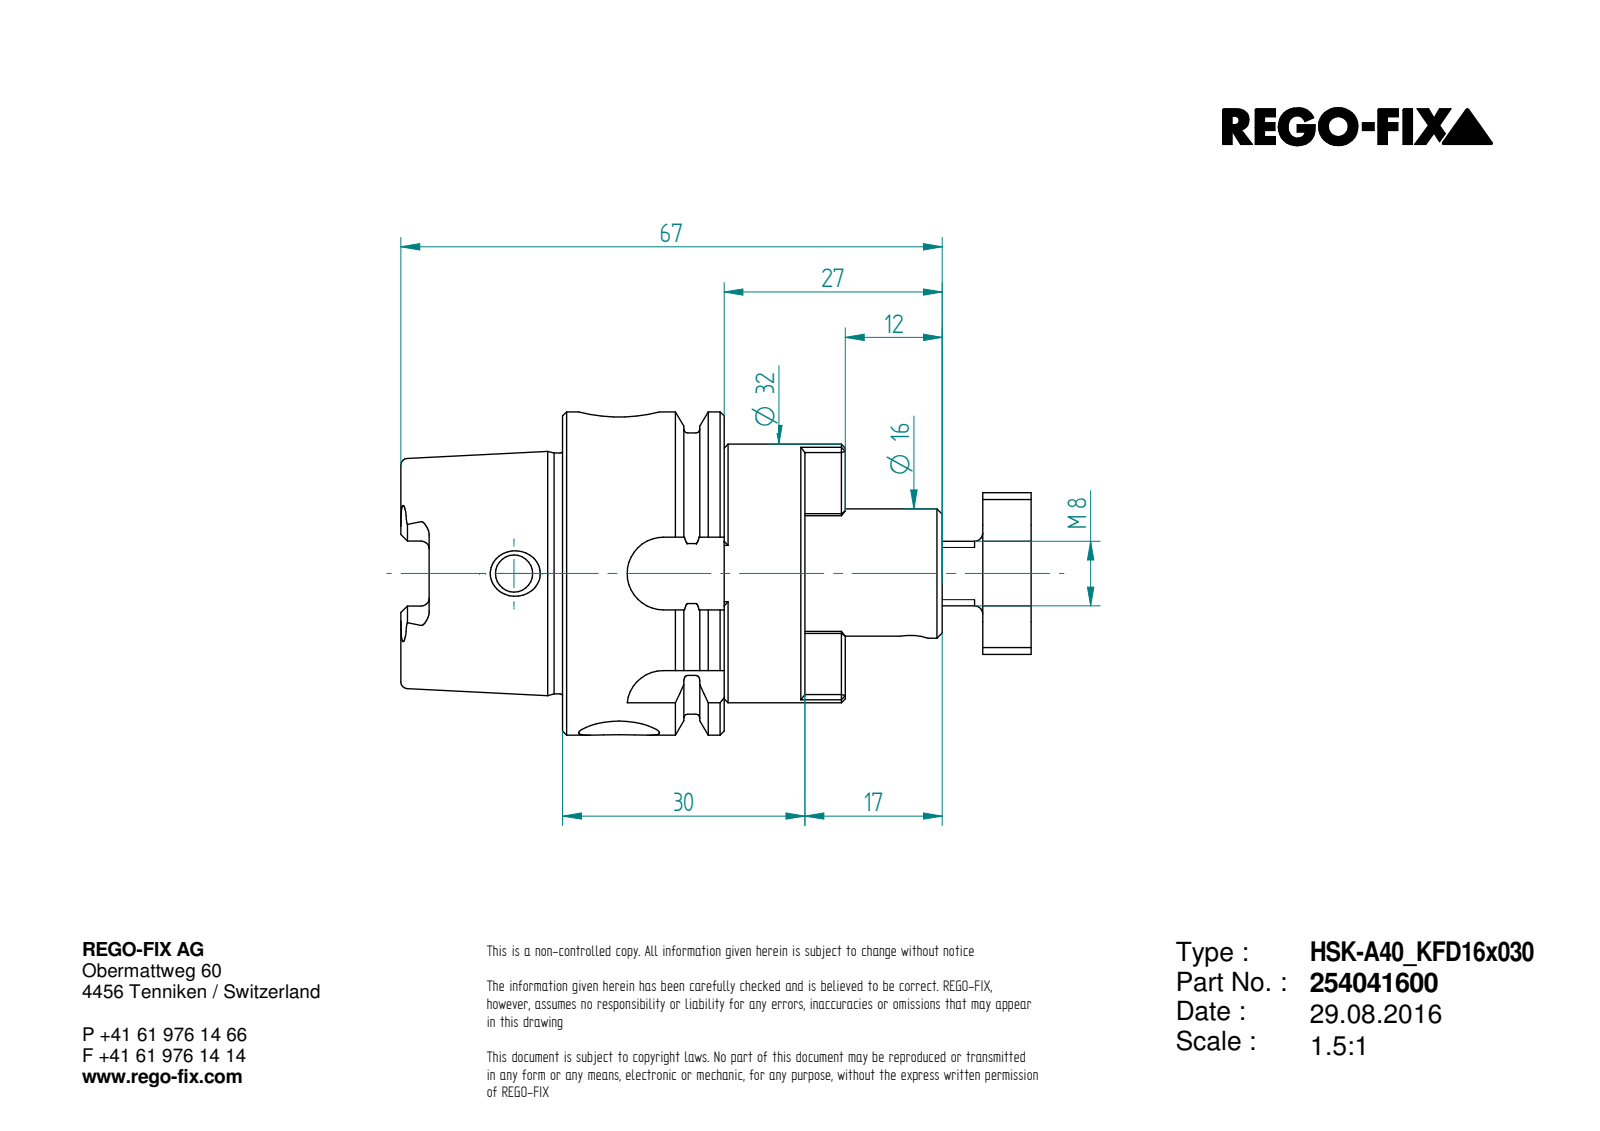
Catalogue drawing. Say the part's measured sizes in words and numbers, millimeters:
Its 3-D file was written by "Unknown (AUTOMOTIVE_DESIGN)". It is 4 solids with 264 faces: 135 planar, 52 cylindrical and 77 other. Overall it measures 78 by 40 by 40 millimeters. Its volume is 48 518 cubic millimeters and its surface area 19 423 square millimeters. Round holes: 2 of diameter 10, 1 of diameter 4.6, 1 of diameter 5, 1 of diameter 6.65, 1 of diameter 8.4, 1 of diameter 10.92, 1 of diameter 13, 1 of diameter 16, 1 of diameter 21, 1 of diameter 25.5. Round bosses or shafts: 1 of diameter 40, 1 of diameter 34.8, 1 of diameter 32, 1 of diameter 29.8, 1 of diameter 15.6, 1 of diameter 8. Partial cylindrical surfaces (rounded edges, fillets, slot ends): 6 of radius 1, 6 of radius 2, 4 of radius 1.88, 4 of radius 4.5, 1 of radius 4, 1 of radius 10. The main face-to-face distances are 14.8, 20, 8, 10, 30, 15, 22, 24.8, 28, 5.2.
